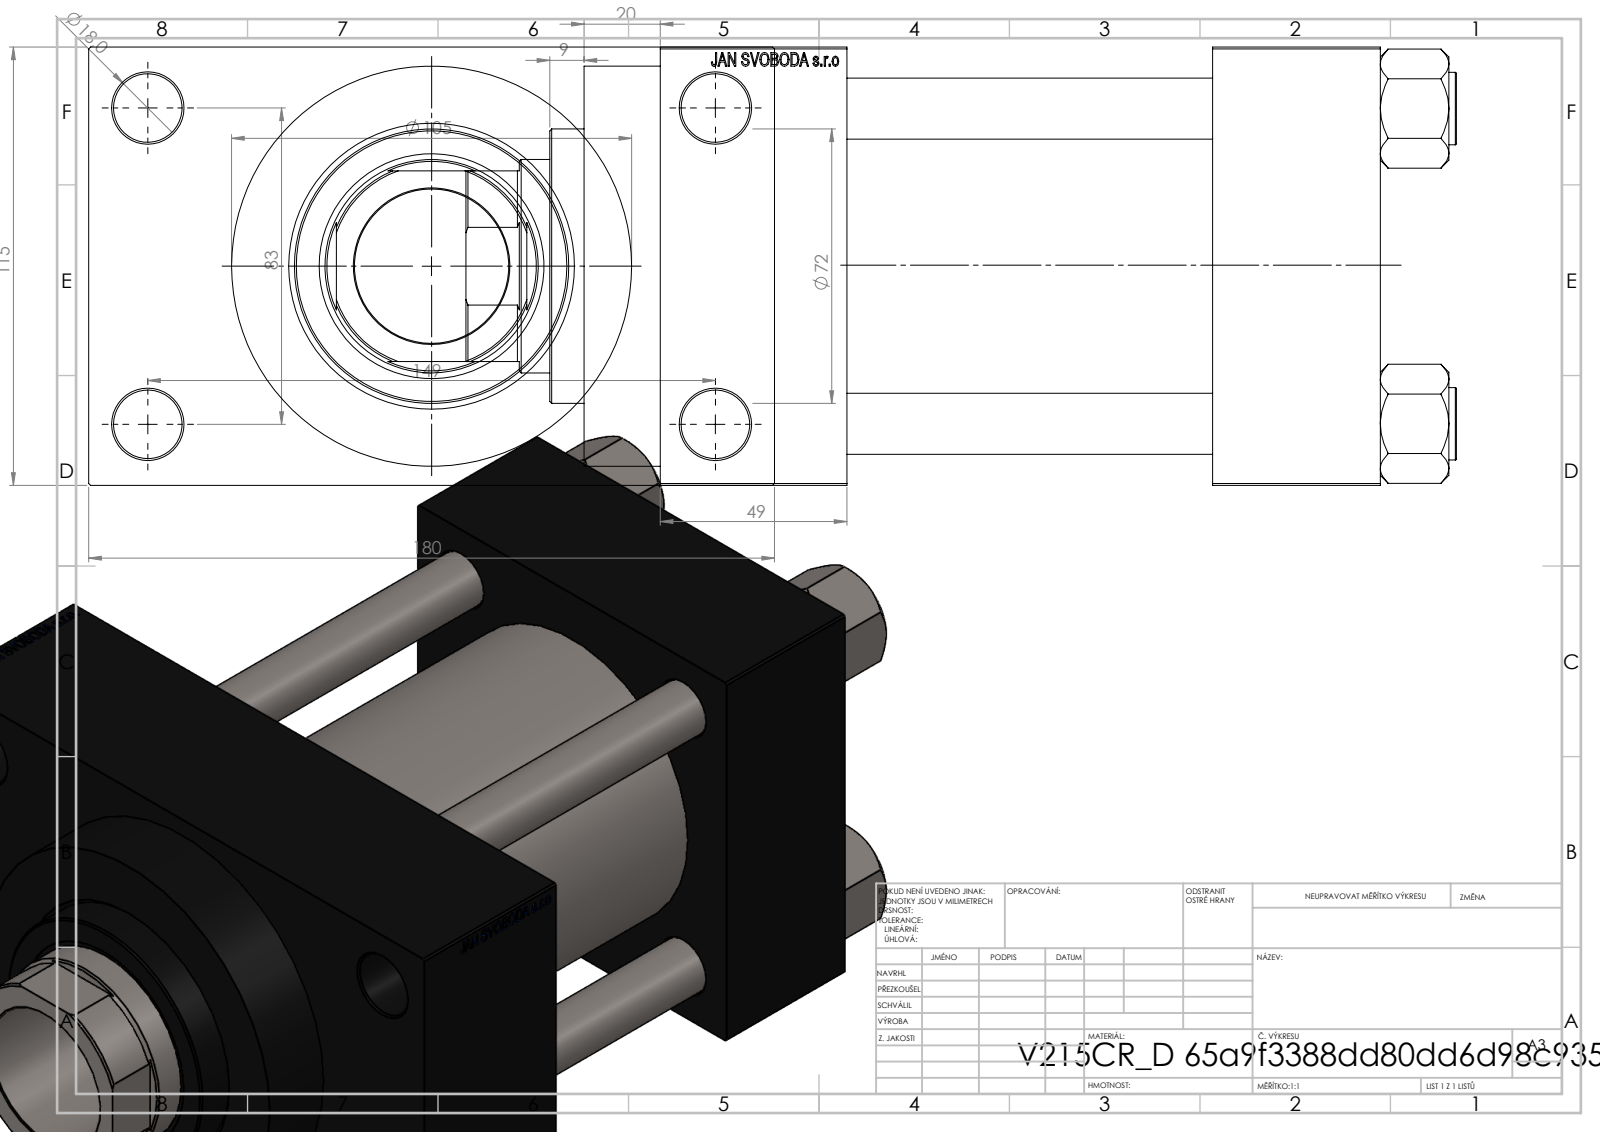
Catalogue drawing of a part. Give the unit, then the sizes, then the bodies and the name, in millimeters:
Units: millimetres
Overall size (bounding box): 260 × 180 × 115
Round holes (diameter × count): ⌀16 ×4, ⌀18 ×4, ⌀7 ×2, ⌀26.44 ×2, ⌀35 ×2, ⌀40.5 ×1, ⌀56 ×1, ⌀59 ×1, ⌀61 ×1, ⌀72 ×1, ⌀80 ×1
Round bosses / shafts (diameter × count): ⌀19 ×4, ⌀105 ×1, ⌀86 ×1
Partial cylindrical surfaces — rounded edges, fillets, slot ends (radius × count): R27 ×1
Main face-to-face distances: 115, 96, 44, 140, 189, 145, 49, 32.5, 147.5, 20
Hole centre spacings: 33.15, 58.48, 82.7, 85.28, 89.24, 115.85, 142.43, 83
Volume: 2 223 000 mm³ · Surface area: 337 495 mm²
Bodies: 11 solids, 1150 faces (544 planar, 86 cylindrical, 520 other)
Part name (STEP PRODUCT): NUT_M5_D; V215CR_VCP_D; V215CR_D_TYCINKA; V215_VC_A (+1 more)
STEP written by: SolidWorks 2019 (CONFIG_CONTROL_DESIGN)
